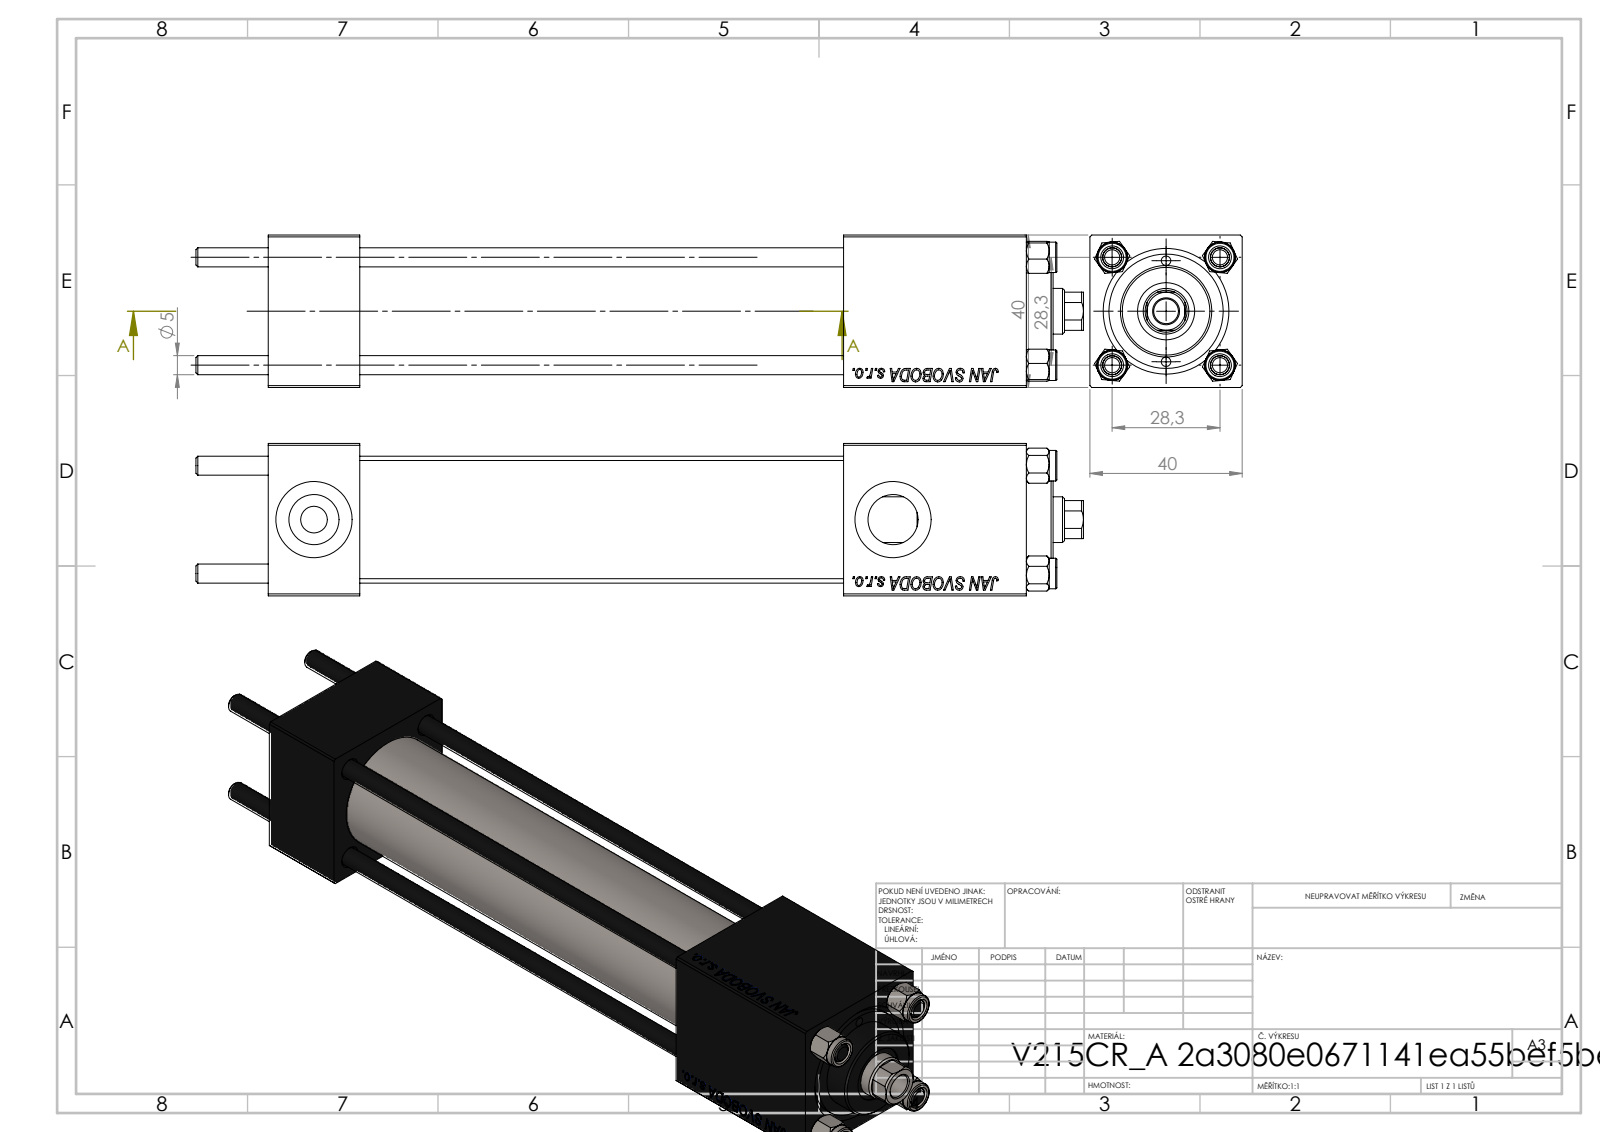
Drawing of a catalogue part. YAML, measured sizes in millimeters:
part_name: "NUT_M5; CR025_012_A_0_G_A_G_M_020_+#_##_TYCINKA; V215CR_VCP; V215_VC_A (+1 more)"
step_written_by: "SolidWorks 2019 (CONFIG_CONTROL_DESIGN)"
units: millimeters
bodies: {solids: 11, faces: 1137, planar: 519, cylindrical: 82, other: 536}
overall_size: [233, 40, 40]
volume: 181217
surface_area: 81067
round_holes:
  - {diameter: 5, count: 4}
  - {diameter: 20, count: 3}
  - {diameter: 2.5, count: 2}
  - {diameter: 7, count: 2}
  - {diameter: 13.16, count: 2}
  - {diameter: 6.5, count: 1}
  - {diameter: 12, count: 1}
  - {diameter: 15, count: 1}
  - {diameter: 25, count: 1}
  - {diameter: 30, count: 1}
round_bosses_or_shafts:
  - {diameter: 8, count: 4}
  - {diameter: 31, count: 1}
  - {diameter: 24, count: 1}
partial_cylinders:
  - {radius: 5.5, count: 1}
face_to_face_distances: [40, 24, 170.3, 146.3, 199, 175, 28.7, 151, 127, 19.3]
hole_center_spacings: [14.18, 20.01, 28.3, 30.84, 13.25, 40.02, 26.5, 152]
